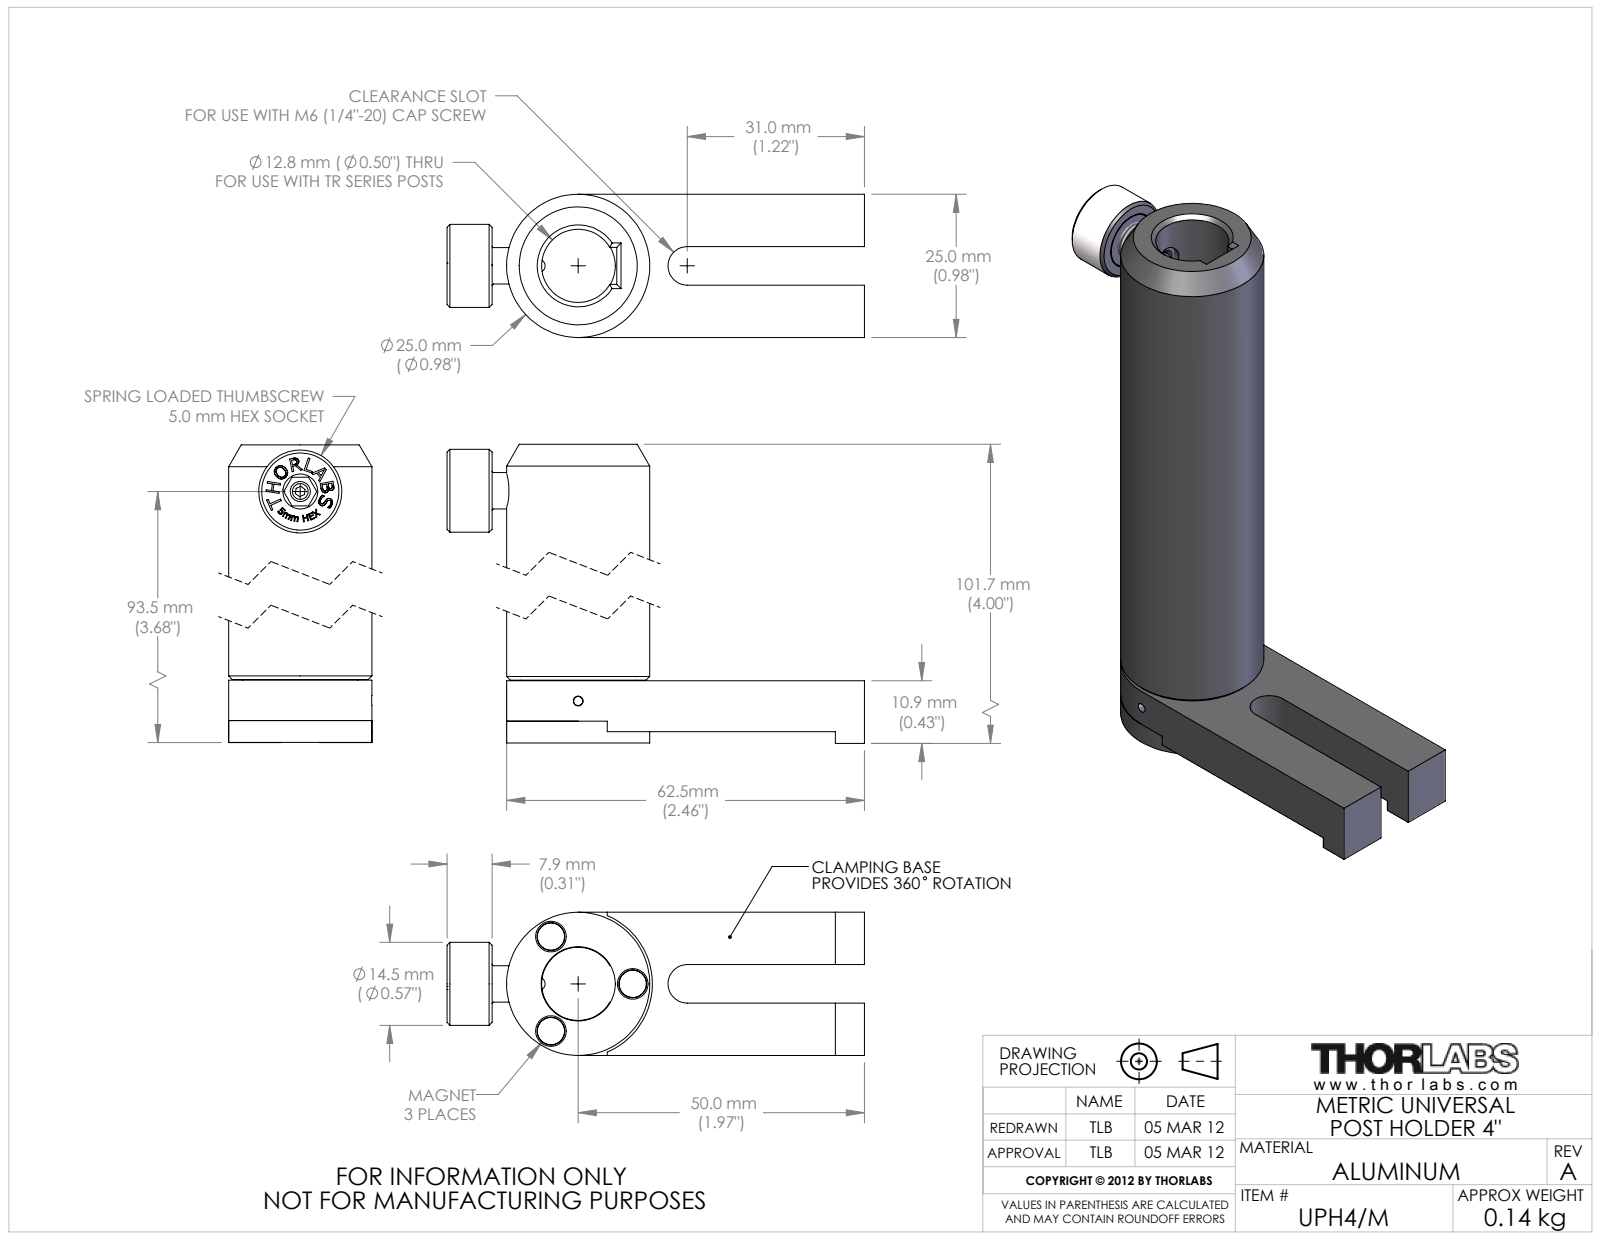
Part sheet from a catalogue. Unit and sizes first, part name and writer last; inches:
Units: inches
Overall size (bounding box): 4.004 × 2.871 × 0.984
Round holes (diameter × count): ⌀0.19 ×3, ⌀0.063 ×1, ⌀0.067 ×1, ⌀0.07 ×1, ⌀0.084 ×1, ⌀0.1 ×1, ⌀0.125 ×1, ⌀0.138 ×1, ⌀0.201 ×1, ⌀0.4 ×1, ⌀0.503 ×1, ⌀0.51 ×1
Round bosses / shafts (diameter × count): ⌀0.187 ×3, ⌀0.984 ×1, ⌀0.79 ×1, ⌀0.7 ×1, ⌀0.68 ×1, ⌀0.57 ×1, ⌀0.39 ×1, ⌀0.25 ×1
Partial cylindrical surfaces — rounded edges, fillets, slot ends (radius × count): R0.133 ×1, R0.51 ×1
Main face-to-face distances: 0.35, 0.359, 0.625, 0.984, 0.072, 0.278, 0.078, 0.15, 0.428, 0.265
Hole centre spacings: 0.375, 0.649, 0.65, 3.377
Volume: 2.701 in³ · Surface area: 31.39 in²
Bodies: 10 solids, 436 faces (211 planar, 84 cylindrical, 141 other)
Part name (STEP PRODUCT): 21066-E0W
STEP written by: SolidWorks 2011 (AUTOMOTIVE_DESIGN)
